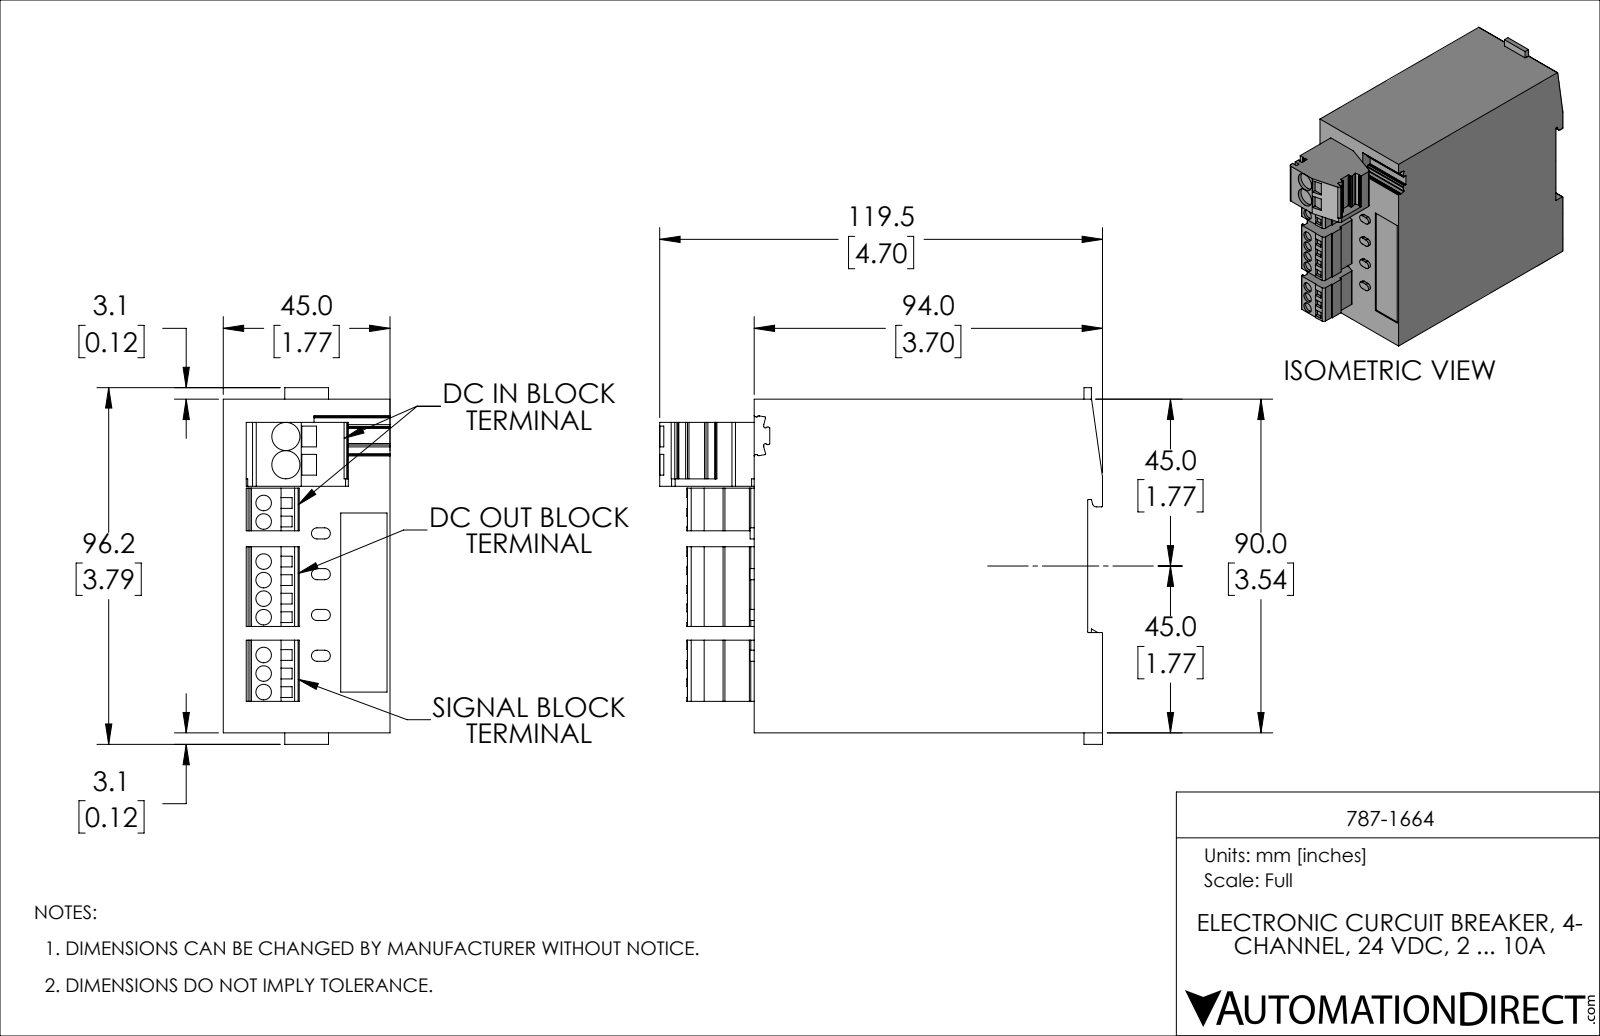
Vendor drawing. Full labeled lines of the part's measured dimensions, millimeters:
Part name (STEP PRODUCT): 787-1664
STEP written by: PARTsolutions (CONFIG_CONTROL_DESIGN)
Units: millimetres
Bodies: 1 solid, 328 faces (248 planar, 80 cylindrical, 0 other)
Overall size (bounding box): 119.5 × 96.2 × 45
Volume: 393 125 mm³ · Surface area: 41 275 mm²
Round holes (diameter × count): ⌀4.2 ×9, ⌀7.6 ×2
Partial cylindrical surfaces — rounded edges, fillets, slot ends (radius × count): R0.2 ×25, R1.5 ×8, R1 ×7, R0.4 ×6, R0.3 ×4, R0.49 ×4, R2 ×1
Main face-to-face distances: 45, 90, 4, 94, 0.5, 38.8, 6.2, 23.5, 66.5, 16.5
Hole centre spacings: 5, 10, 20.2, 25.2, 15.2, 15.8, 20.8, 25.8
